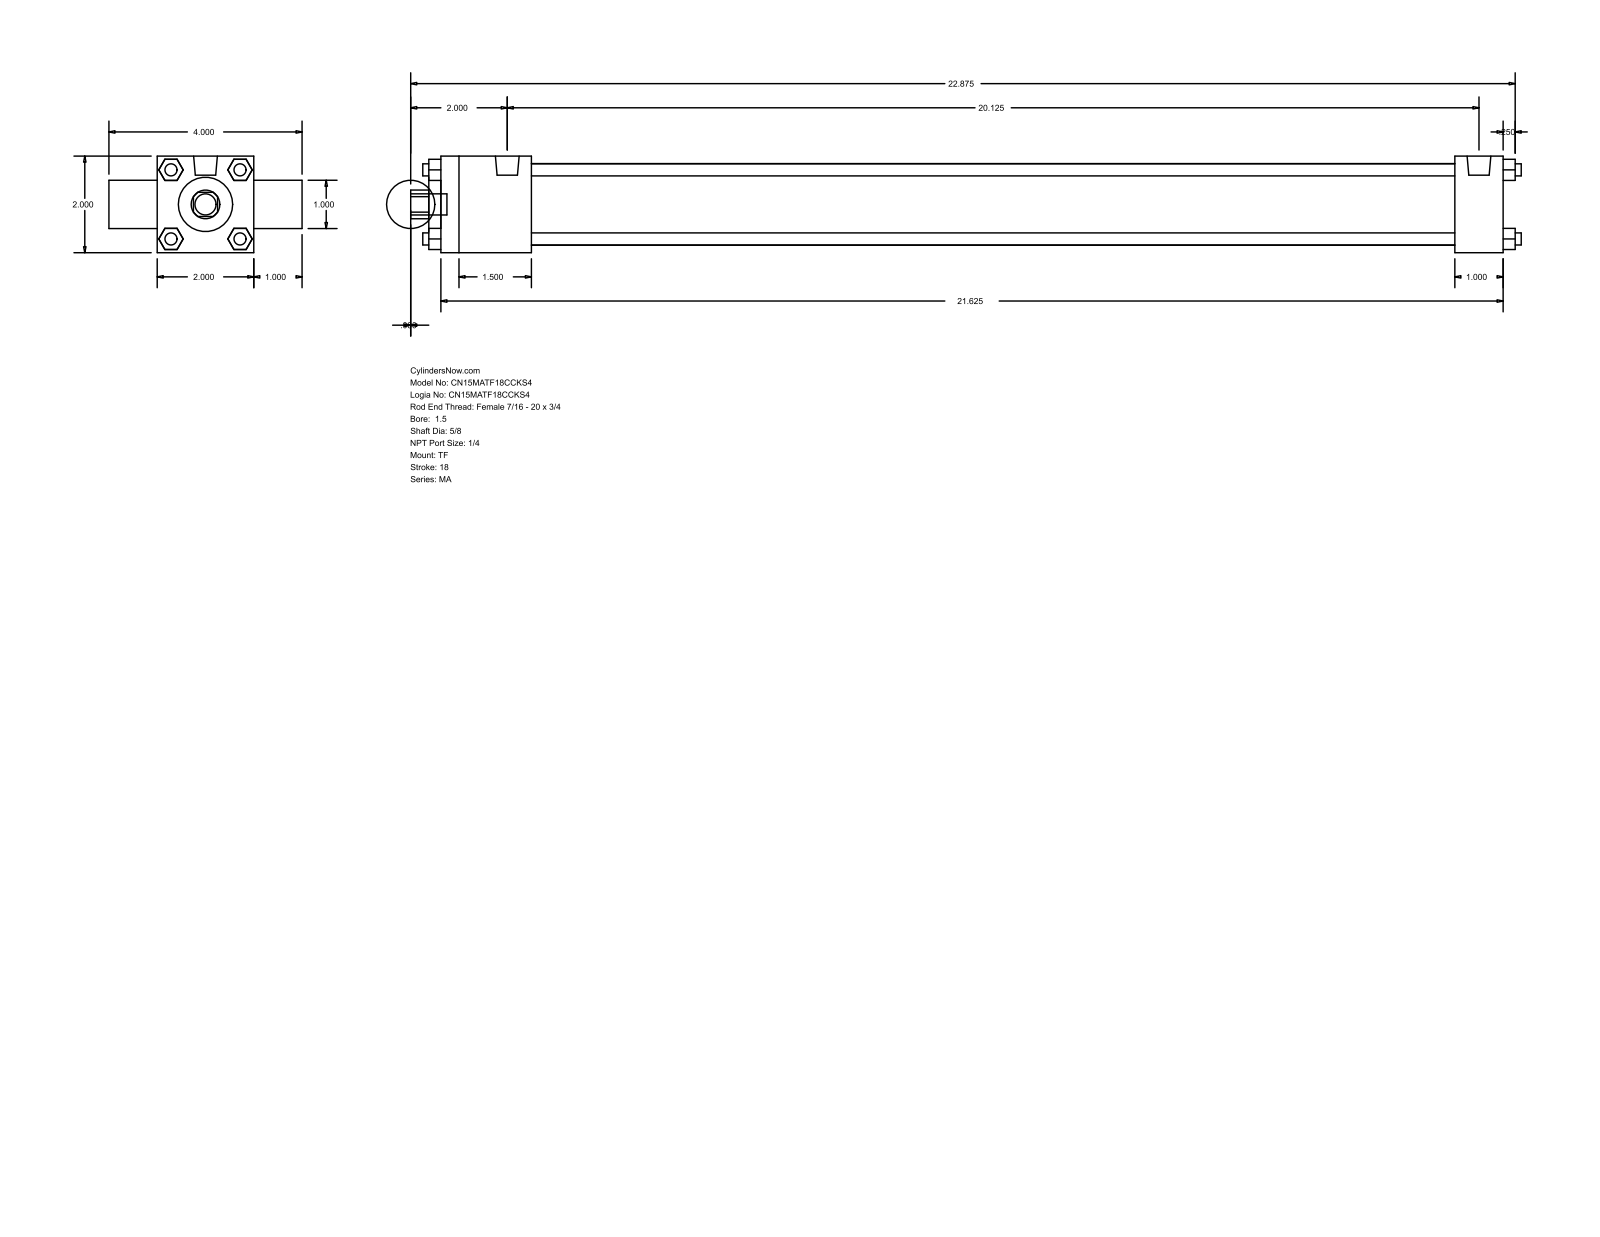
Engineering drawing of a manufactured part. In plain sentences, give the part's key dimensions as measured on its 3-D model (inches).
The part is named "MA_TF__0150_0.625". Its 3-D file was written by "GSSL Pune (CONFIG_CONTROL_DESIGN)". It is 0 solids with 120 faces: 92 planar, 28 cylindrical and 0 other. Overall it measures 23 by 4 by 2 inches. Round holes: 1 of diameter 0.625, 1 of diameter 1, 1 of diameter 1.125, 1 of diameter 1.69. Round bosses or shafts: 4 of diameter 0.25, 3 of diameter 0.313, 2 of diameter 0.492, 1 of diameter 0.437. Partial cylindrical surfaces (rounded edges, fillets, slot ends): 1 of radius 0.297. The main face-to-face distances are 2, 1, 22, 0.25, 22.25, 3, 1.875, 21, 19.125, 20.125.
